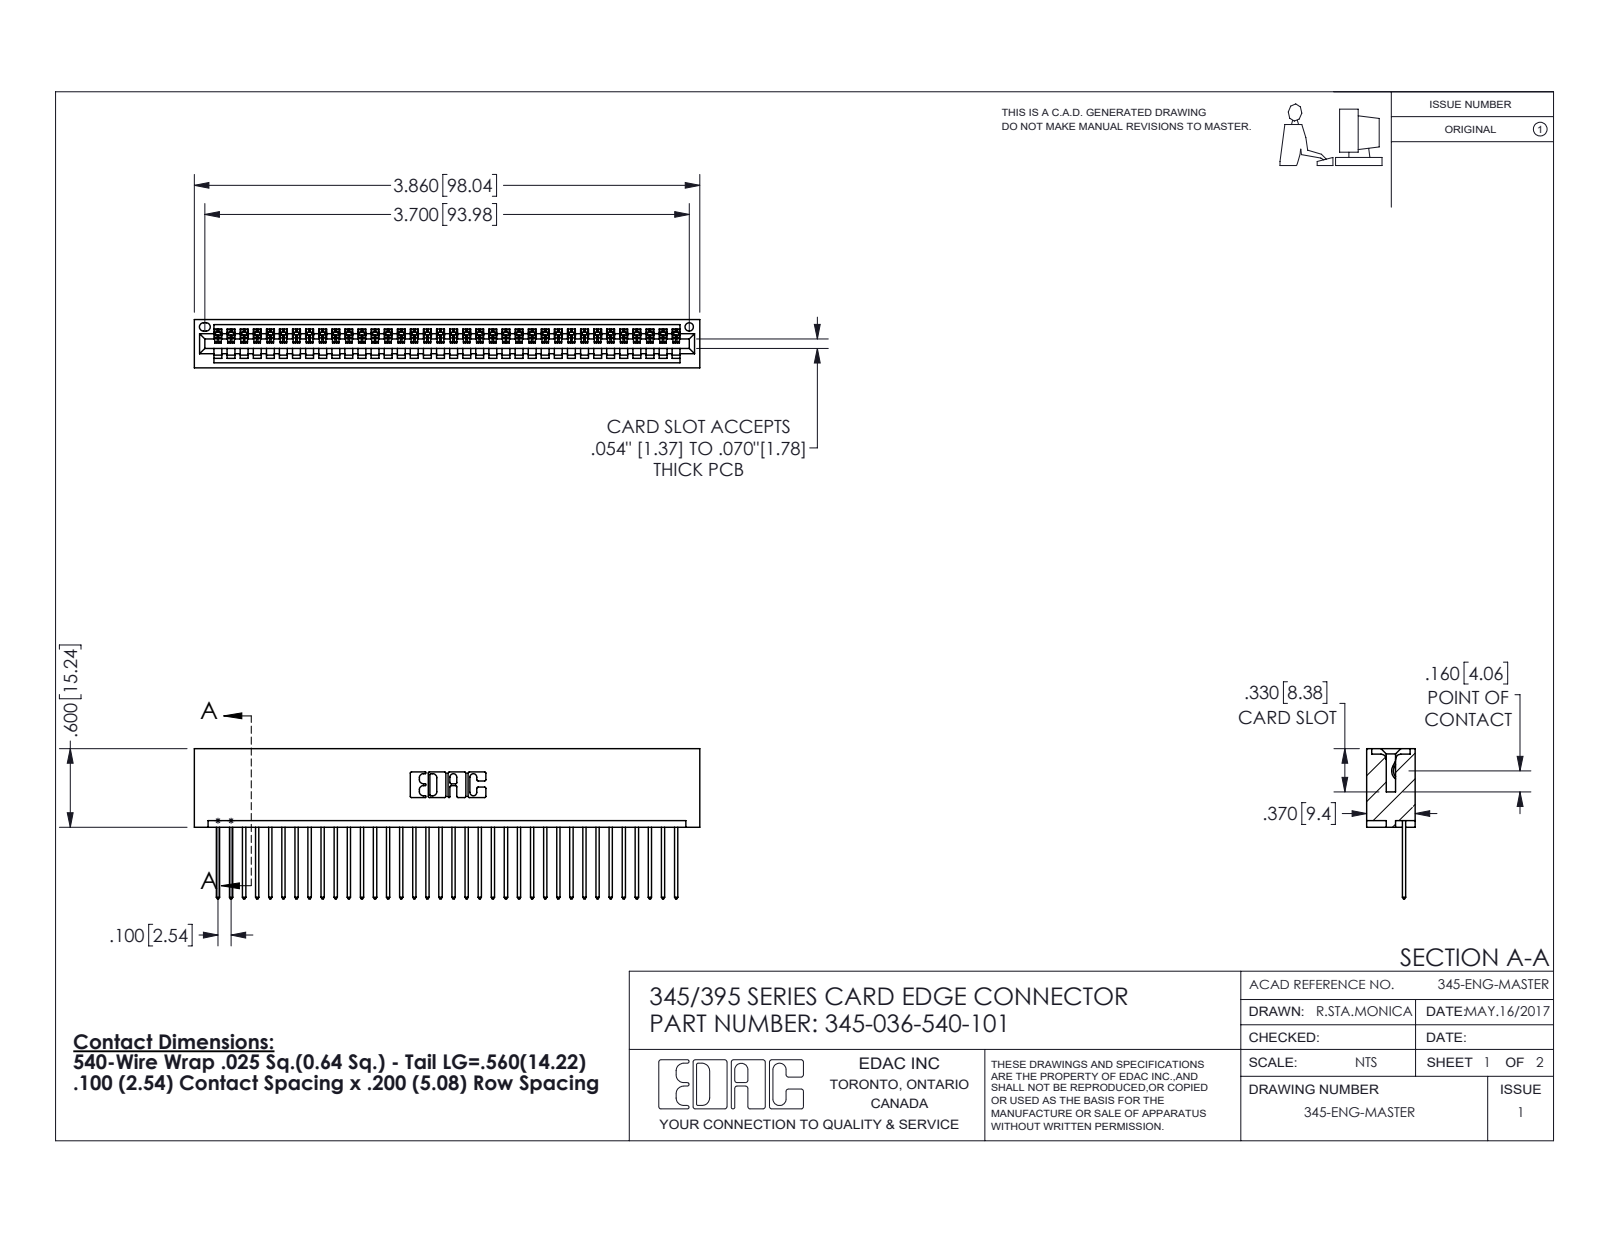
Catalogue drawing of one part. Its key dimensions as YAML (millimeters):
part_name: "345-292-001_345-293-140; 345-036-540-101; 345 Part_No Mounting Lugs"
step_written_by: "SolidWorks 2016 (CONFIG_CONTROL_DESIGN)"
units: millimeters
bodies: {solids: 37, faces: 2206, planar: 1516, cylindrical: 690, other: 0}
overall_size: [98, 29.1, 9.4]
volume: 9900
surface_area: 13610
round_holes:
  - {diameter: 1.6, count: 1}
partial_cylinders:
  - {radius: 0.2, count: 72}
  - {radius: 0.3, count: 72}
  - {radius: 0.3, count: 22}
  - {radius: 0.2, count: 6}
  - {radius: 0.8, count: 6}
  - {radius: 0.7, count: 3}
  - {radius: 0.8, count: 2}
  - {radius: 1, count: 2}
face_to_face_distances: [1.8, 7.6, 2.5, 6.9, 0.6, 9.4, 5.1, 5.7, 3.8, 1.8]
